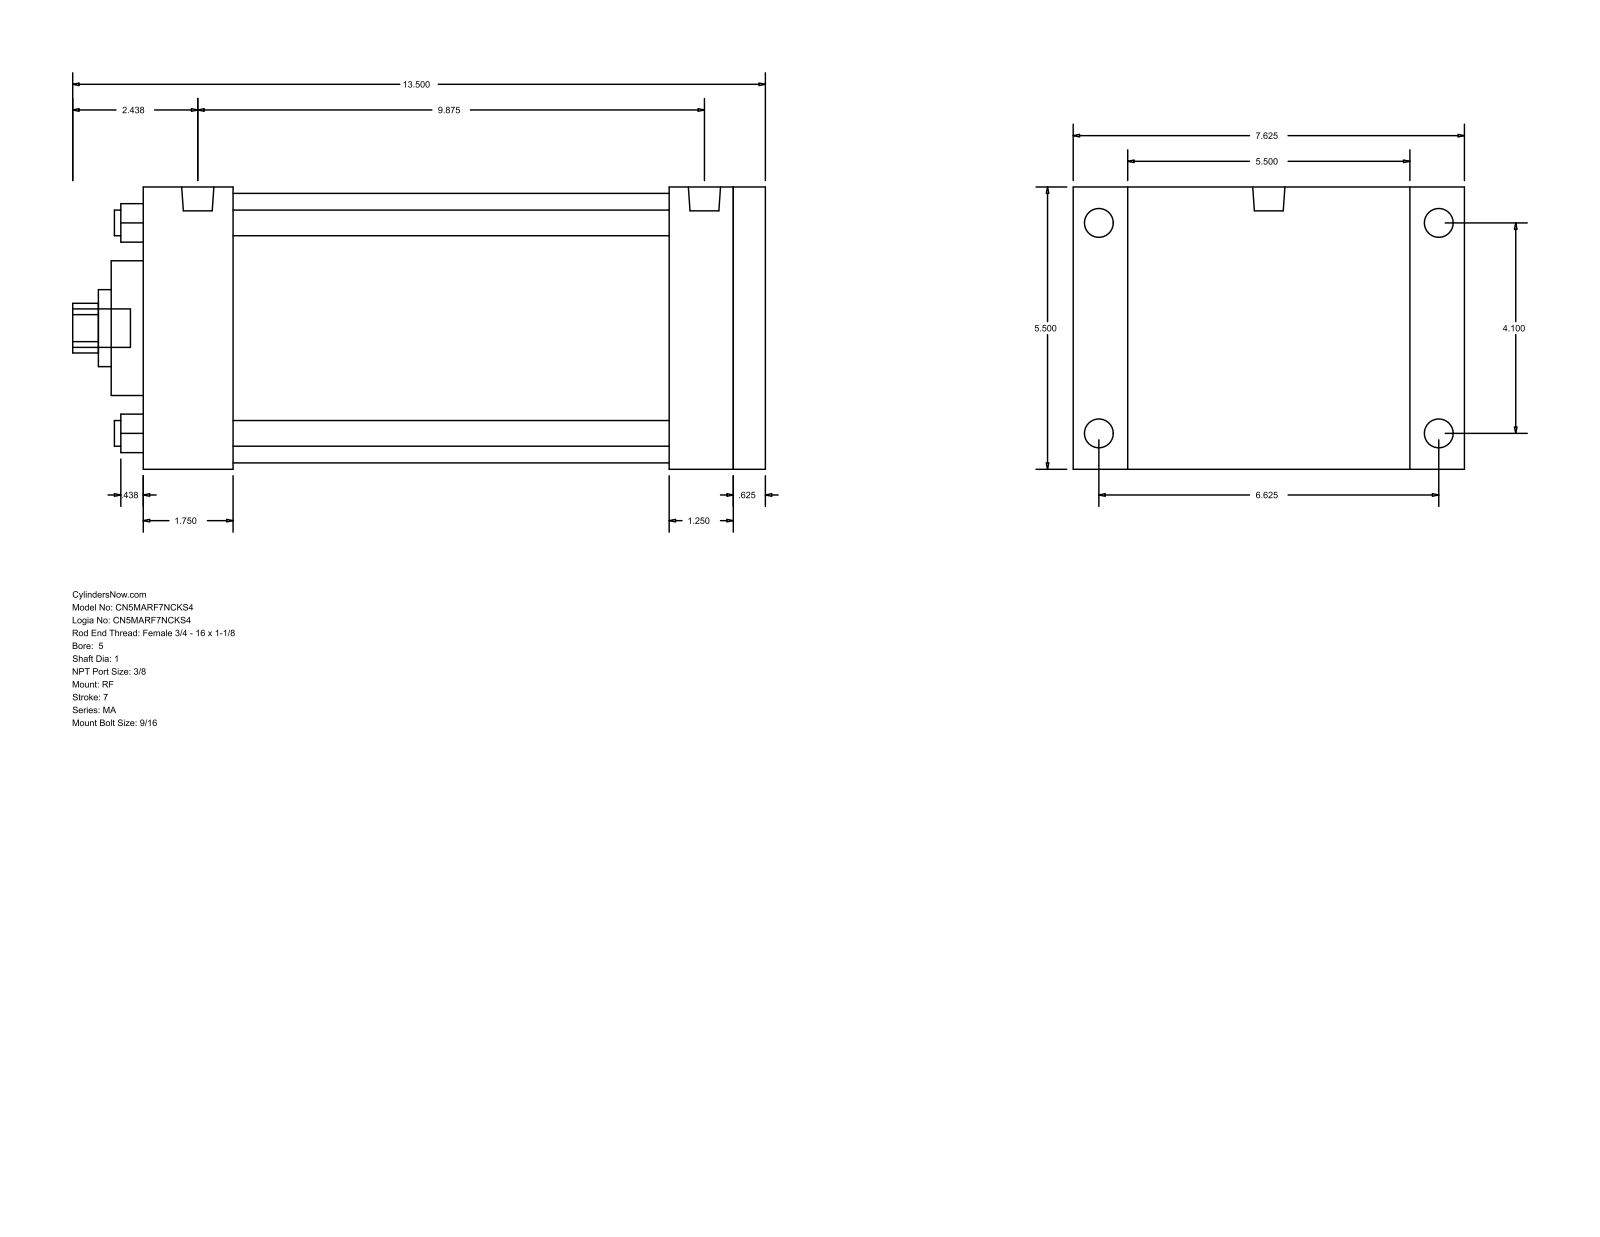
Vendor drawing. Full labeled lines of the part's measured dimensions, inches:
Part name (STEP PRODUCT): MA_RF__0500_1
STEP written by: GSSL Pune (CONFIG_CONTROL_DESIGN)
Units: inches
Bodies: 0 solids, 94 faces (65 planar, 29 cylindrical, 0 other)
Overall size (bounding box): 13.5 × 7.625 × 5.5
Round holes (diameter × count): ⌀0.5 ×4, ⌀1 ×1, ⌀1.5 ×1, ⌀2.625 ×1, ⌀5.25 ×1
Round bosses / shafts (diameter × count): ⌀0.563 ×4, ⌀0.437 ×4, ⌀0.627 ×2, ⌀0.75 ×1
Partial cylindrical surfaces — rounded edges, fillets, slot ends (radius × count): R0.484 ×1
Main face-to-face distances: 5.5, 12.125, 11.5, 0.625, 1.75, 9.75, 10.375, 10.25, 8.5, 1.25
Hole centre spacings: 2.899, 4.1, 5.798
